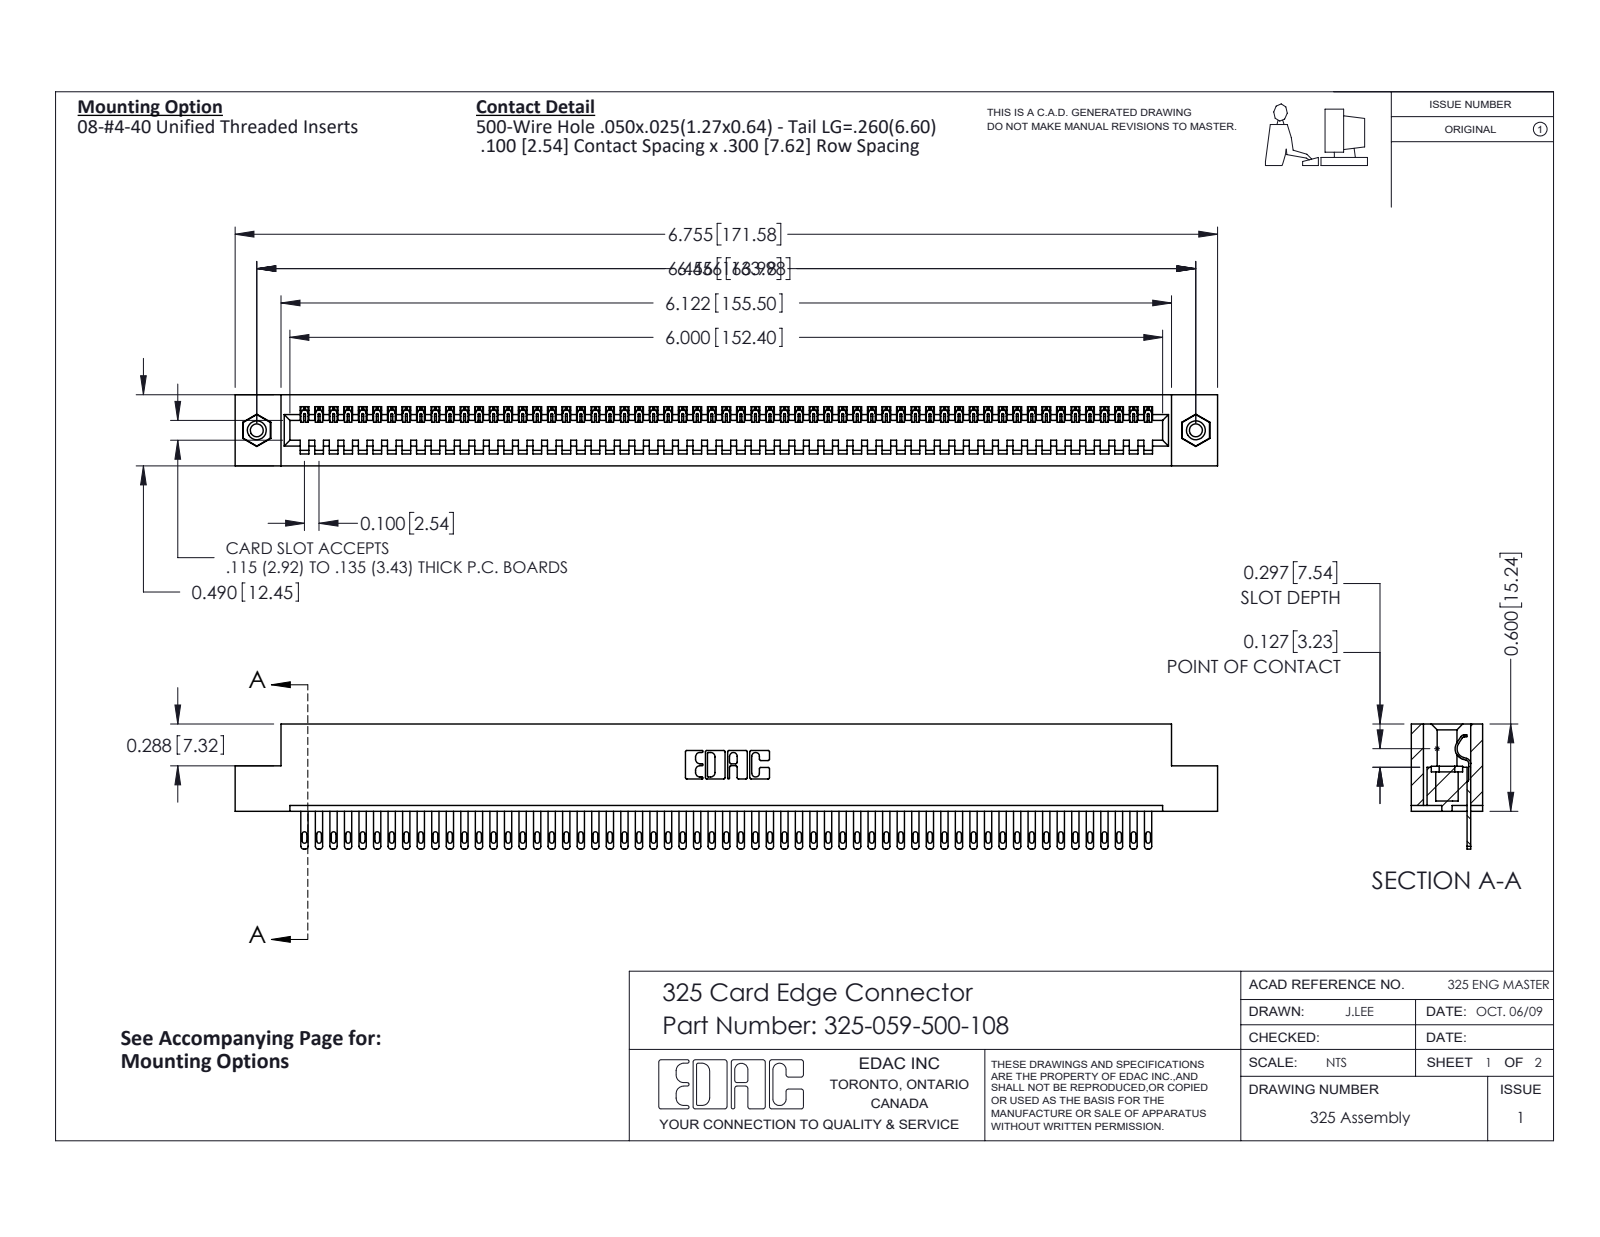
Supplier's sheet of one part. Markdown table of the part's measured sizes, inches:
| quantity | value |
| --- | --- |
| part name | 325-059-500-108; 345-250-001_345-250-003-102; 325 Part_TI; 325-292-001_325-293-100 |
| STEP written by | SolidWorks 2016 (CONFIG_CONTROL_DESIGN) |
| units | inches |
| bodies | 62 solids, 3360 faces (2226 planar, 1118 cylindrical, 16 other) |
| overall size | 6.755 × 0.86 × 0.49 |
| volume | 1.339 in³ |
| surface area | 37.85 in² |
| round holes (diameter × count) | 0.089 × 2, 0.125 × 2, 0.16 × 2 |
| round bosses / shafts (diameter × count) | 0.155 × 2 |
| partial cylindrical surfaces (radius × count) | 0.006 × 118, 0.016 × 118, 0.02 × 118, 0.01 × 22, 0.007 × 6, 0.031 × 6, 0.026 × 3, 0.014 × 1 |
| main face-to-face distances | 0.083, 0.407, 0.3, 0.49, 0.107, 0.383, 0.025, 0.325, 0.56, 0.263 |
| hole center spacings | 6.456 |
